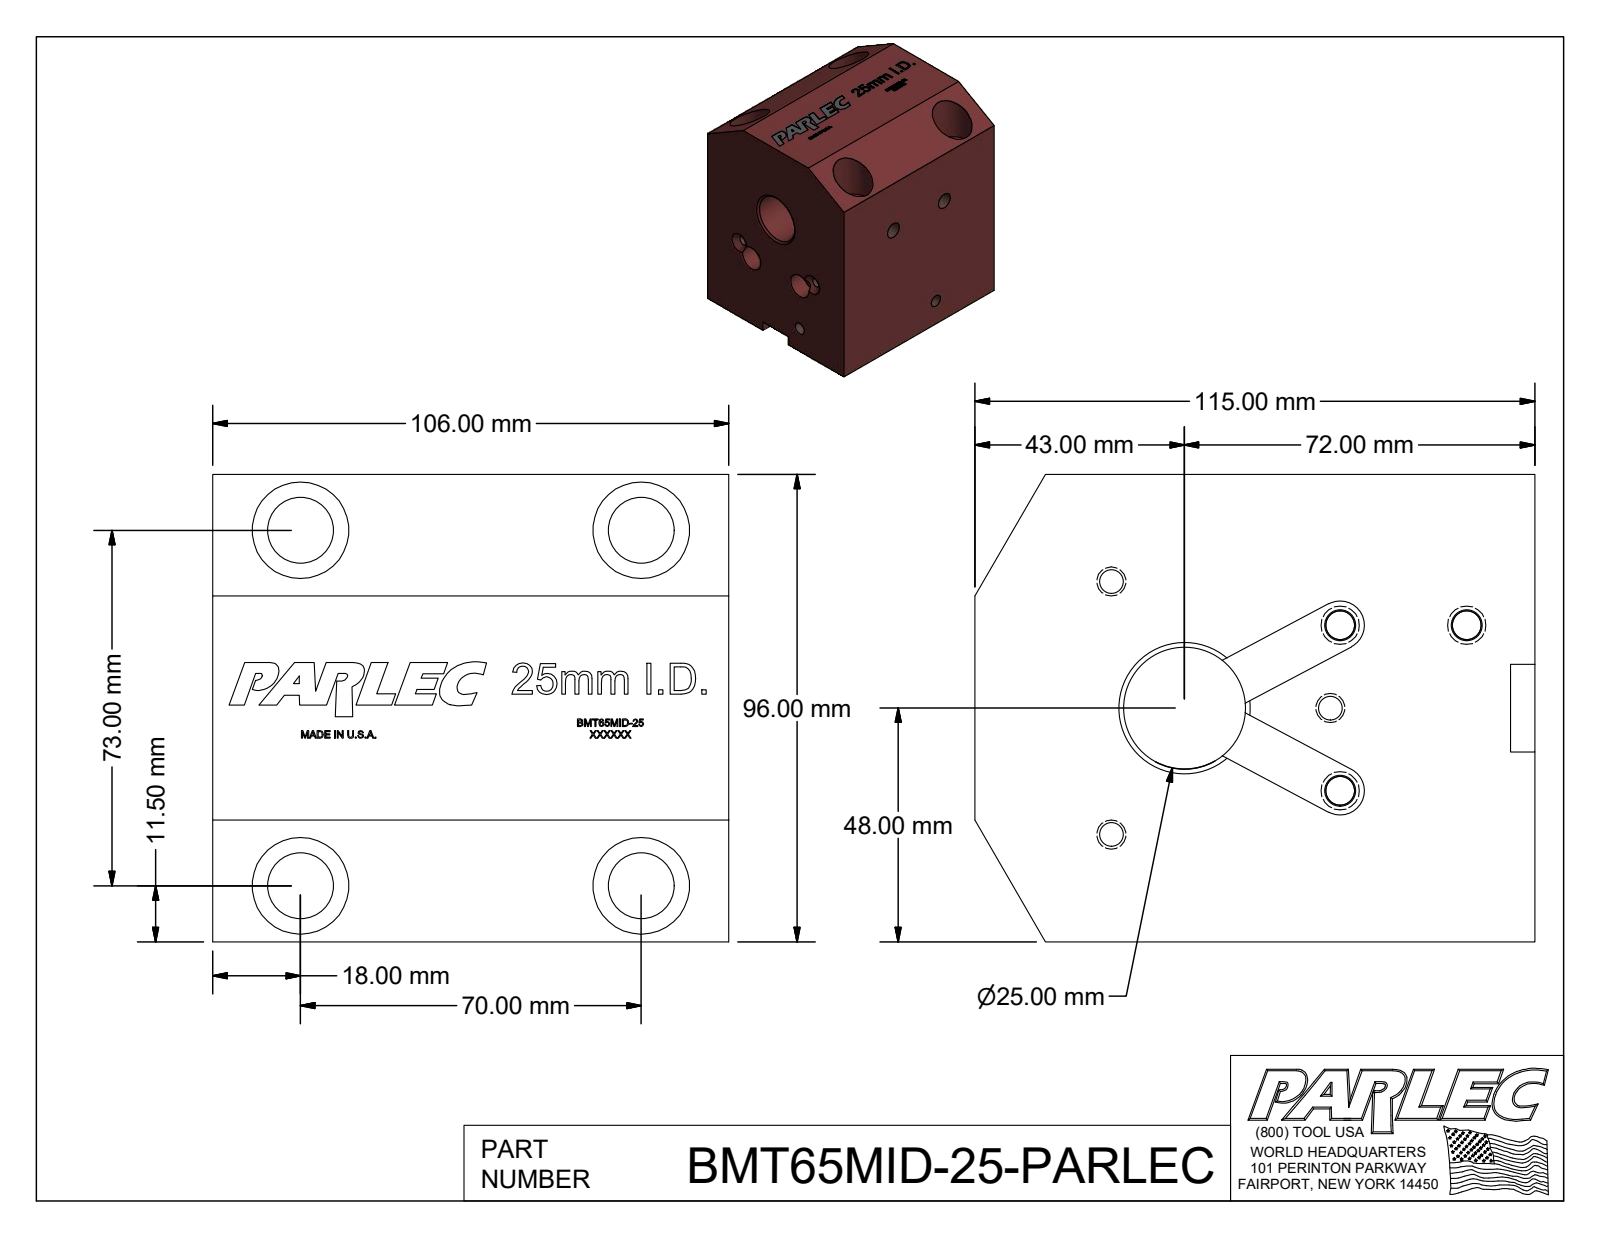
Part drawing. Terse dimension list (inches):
name: BMT65MID-25-PARLEC
written by: Autodesk Inventor 2018 (AUTOMOTIVE_DESIGN)
unit: in
bodies: 1 solid, 785 faces (554 planar, 42 cylindrical, 189 other)
size: 4.528 × 4.173 × 3.78
volume: 59.21 in³; area: 161.6 in²
holes: 8× ⌀0.194, 5× ⌀0.234, 4× ⌀0.531, 4× ⌀0.782, 2× ⌀0.33, 2× ⌀0.339, 2× ⌀0.505, 1× ⌀0.984, 1× ⌀1.044
rounds: 3× R0.354, 2× R0.197
face distances: 3.78, 4.173, 4.528, 0.197, 4.331, 3.543, 3.346, 0.984, 0.118, 4.055
hole spacings: 1.456, 3.319, 1.181, 2.046, 0.394, 0.674, 0.687, 0.772
